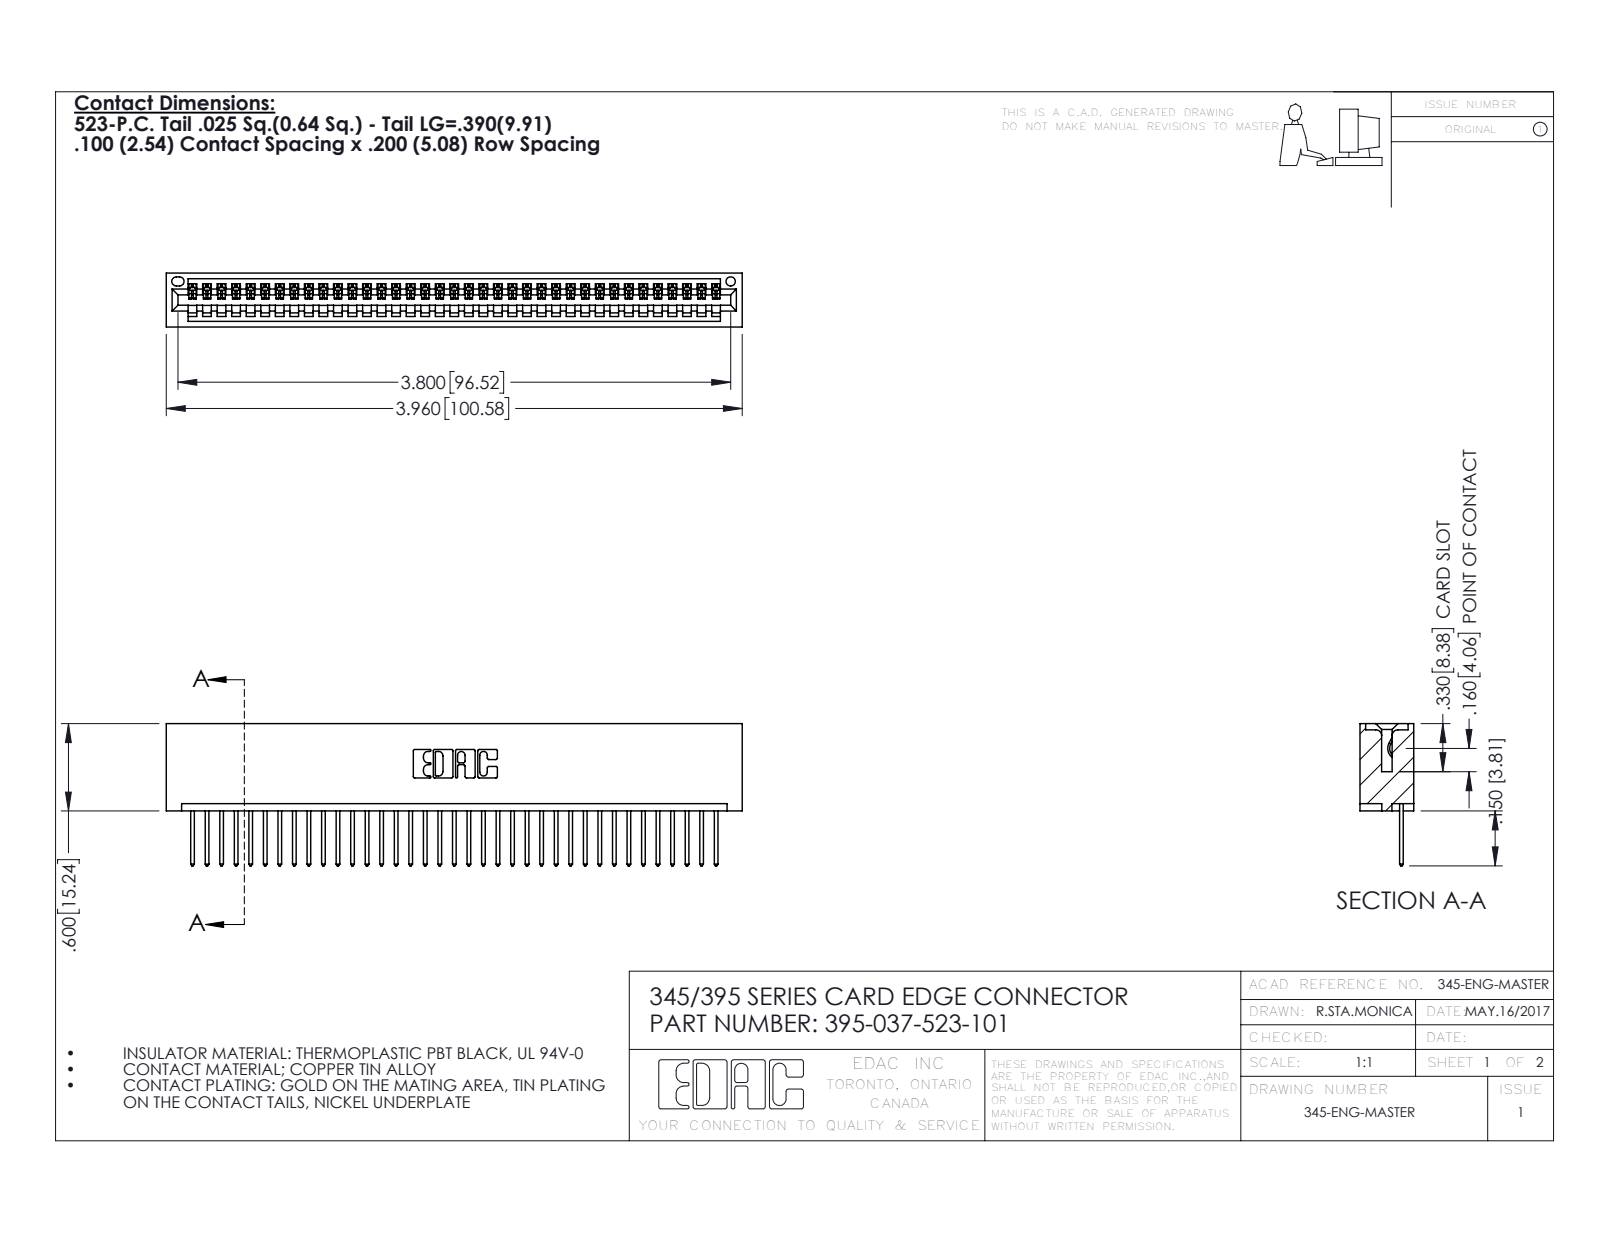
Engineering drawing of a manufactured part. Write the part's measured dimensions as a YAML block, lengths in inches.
part_name: "345 Part_No Mounting Lugs; 345-292-001_345-293-123; 395-037-523-101"
step_written_by: "SolidWorks 2016 (CONFIG_CONTROL_DESIGN)"
units: inches
bodies: {solids: 38, faces: 2264, planar: 1556, cylindrical: 708, other: 0}
overall_size: [3.96, 0.977, 0.37]
volume: 0.615
surface_area: 21.02
round_holes:
  - {diameter: 0.064, count: 1}
partial_cylinders:
  - {radius: 0.006, count: 74}
  - {radius: 0.01, count: 74}
  - {radius: 0.01, count: 22}
  - {radius: 0.007, count: 6}
  - {radius: 0.031, count: 6}
  - {radius: 0.026, count: 3}
  - {radius: 0.031, count: 2}
  - {radius: 0.04, count: 2}
face_to_face_distances: [0.298, 0.072, 0.37, 0.2, 0.098, 0.272, 0.025, 0.225, 0.149, 0.072]
